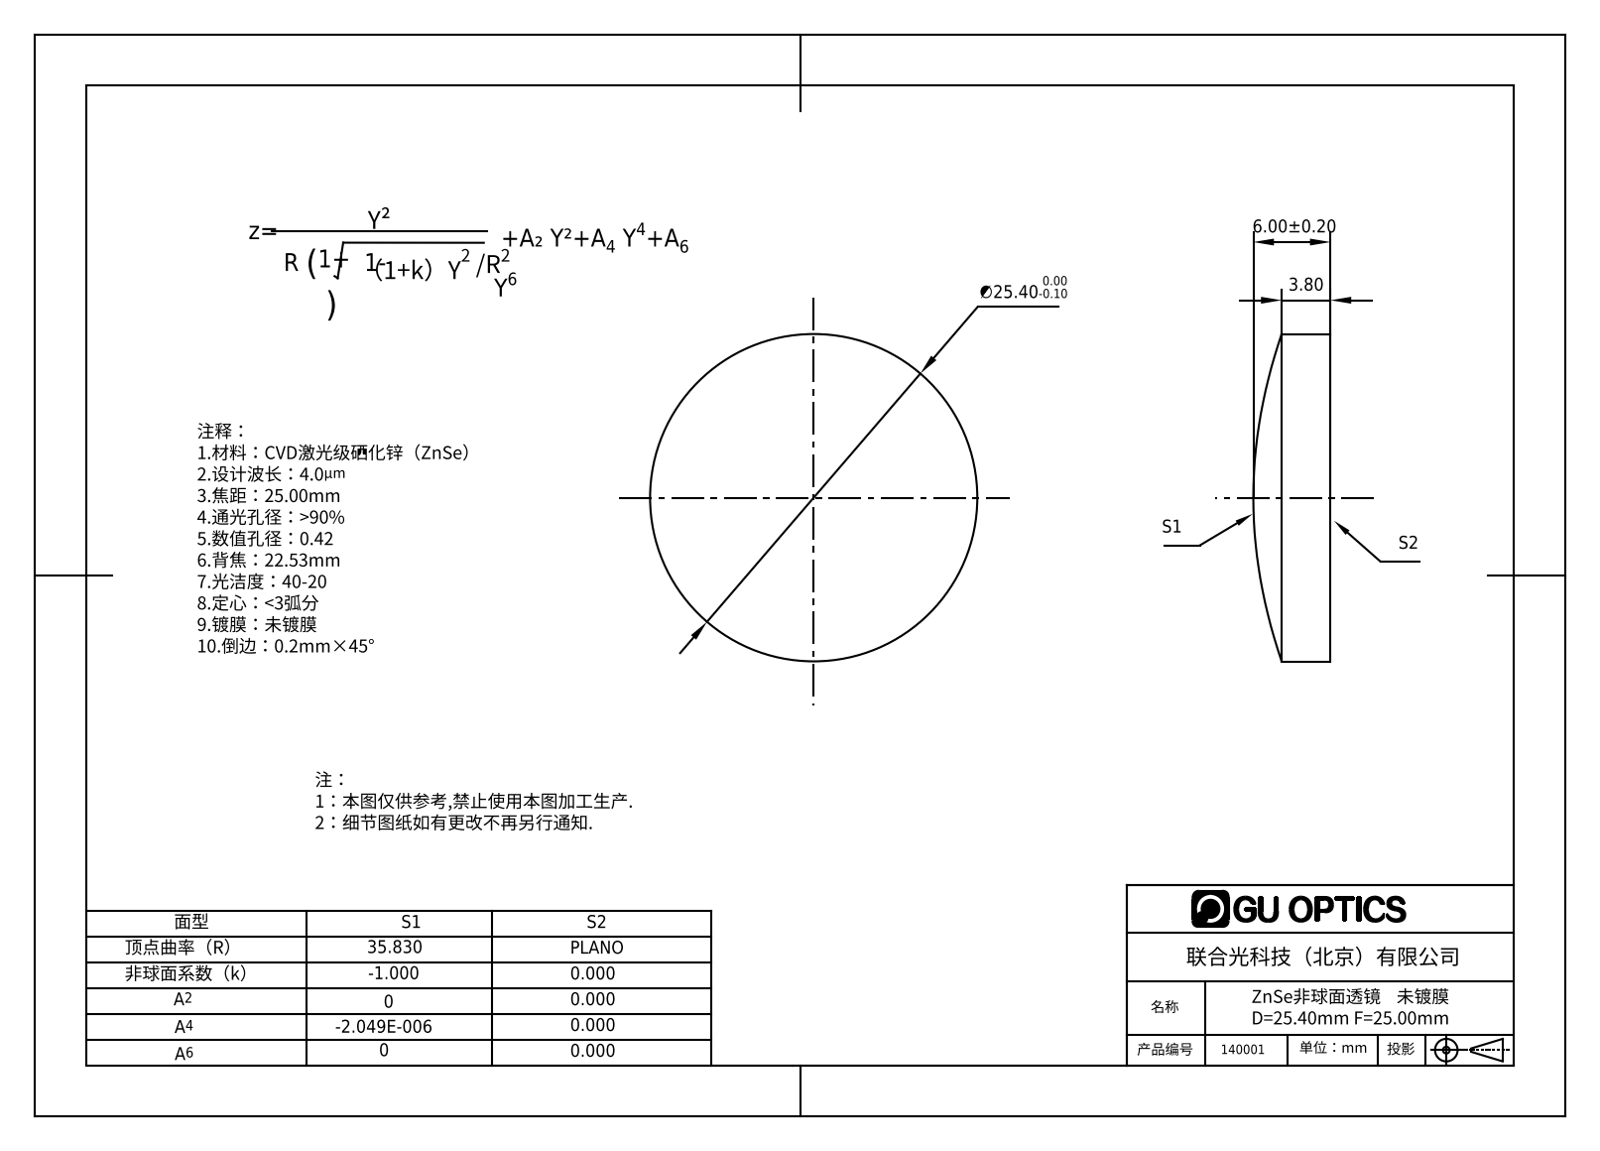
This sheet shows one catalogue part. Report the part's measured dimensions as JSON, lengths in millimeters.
{"part_name": "140001", "step_written_by": "SolidWorks 2020 (CONFIG_CONTROL_DESIGN)", "units": "millimeters", "bodies": {"solids": 1, "faces": 5, "planar": 1, "cylindrical": 2, "other": 2}, "overall_size": [25.4, 25.4, 6], "volume_mm3": 2479, "surface_area_mm2": 1331, "round_bosses_or_shafts": [[25.4, 1]]}
